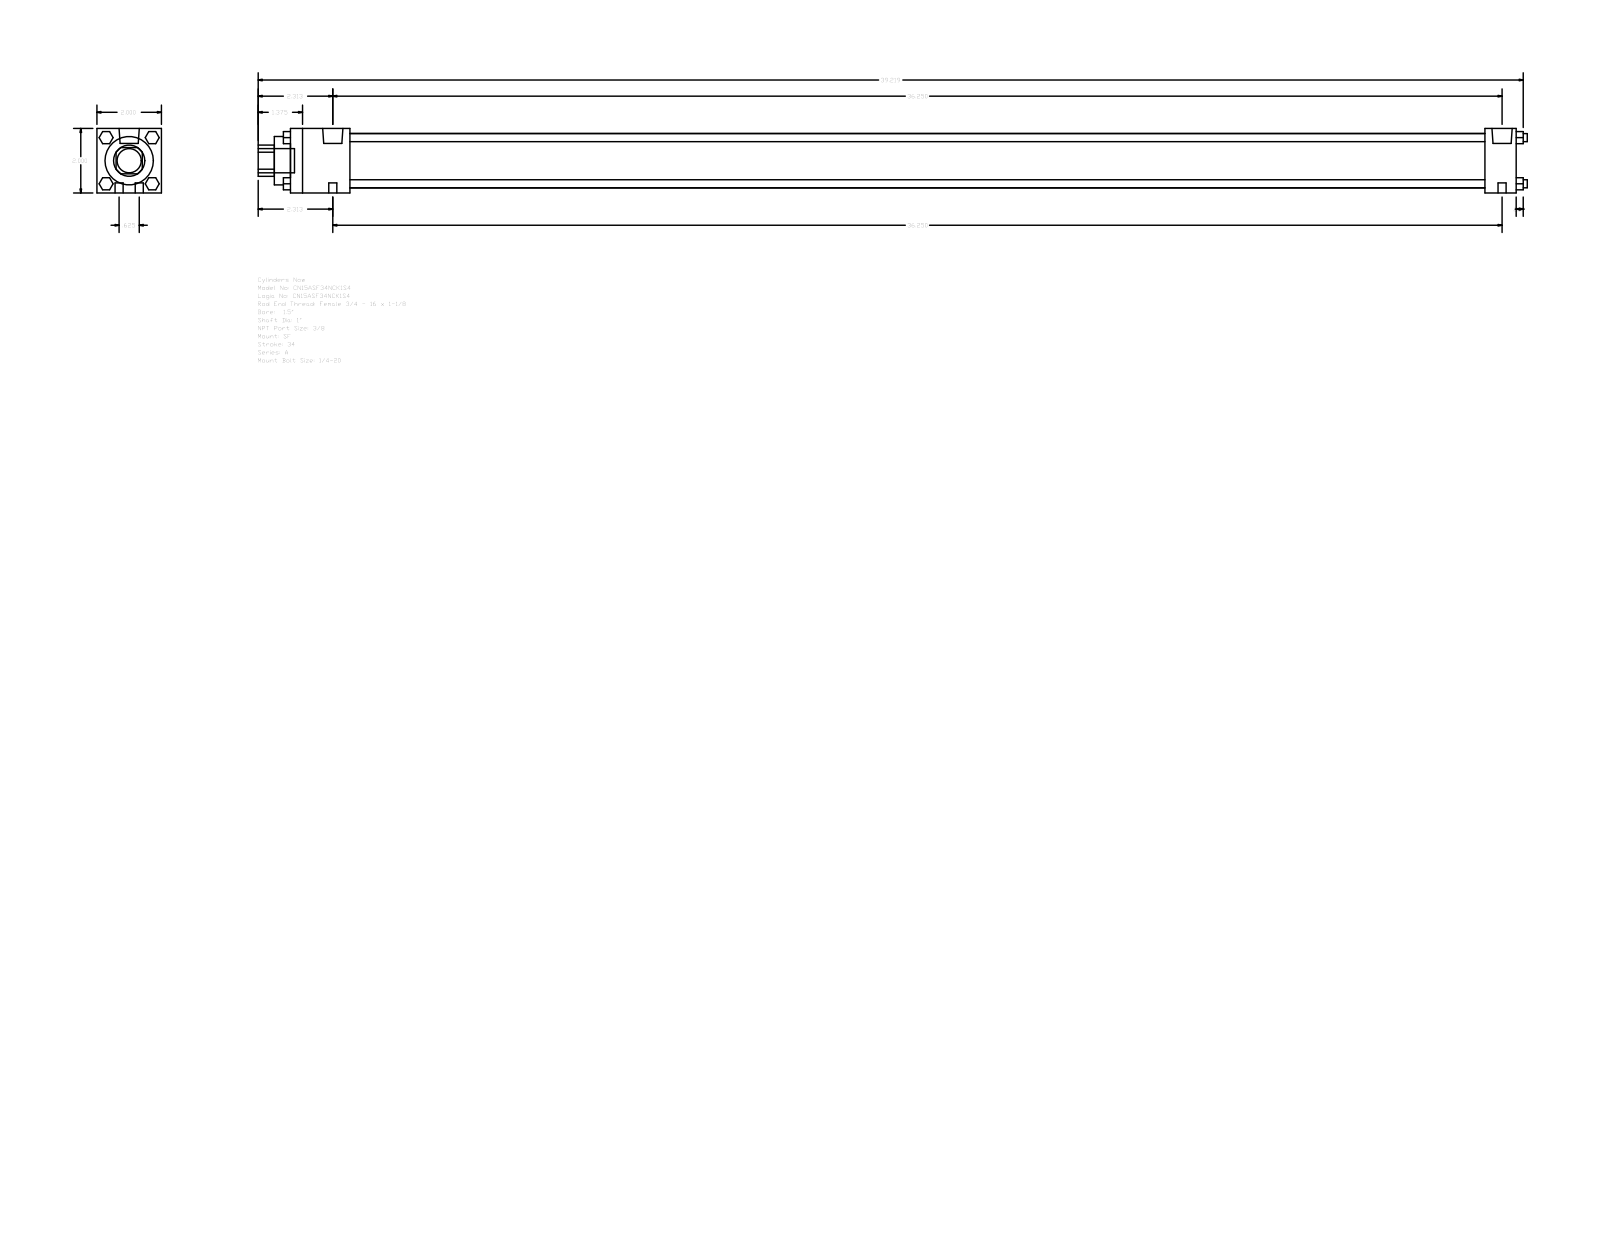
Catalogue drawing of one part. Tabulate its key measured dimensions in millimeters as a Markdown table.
| quantity | value |
| --- | --- |
| part name | A_SF__0150_1 |
| STEP written by | GSSL Pune (CONFIG_CONTROL_DESIGN) |
| units | millimeters |
| bodies | 0 solids, 124 faces (94 planar, 30 cylindrical, 0 other) |
| overall size | 999.33 × 50.8 × 50.8 |
| round holes (diameter × count) | 25.4 × 1, 38.1 × 1, 42.93 × 1 |
| round bosses / shafts (diameter × count) | 6.35 × 8, 15.93 × 2, 5.56 × 2, 19.05 × 1 |
| partial cylindrical surfaces (radius × count) | 12.29 × 1 |
| main face-to-face distances | 50.8, 965.2, 46.83, 940.59, 893.76, 918.37, 24.61, 12.7, 59.53, 953.29 |
